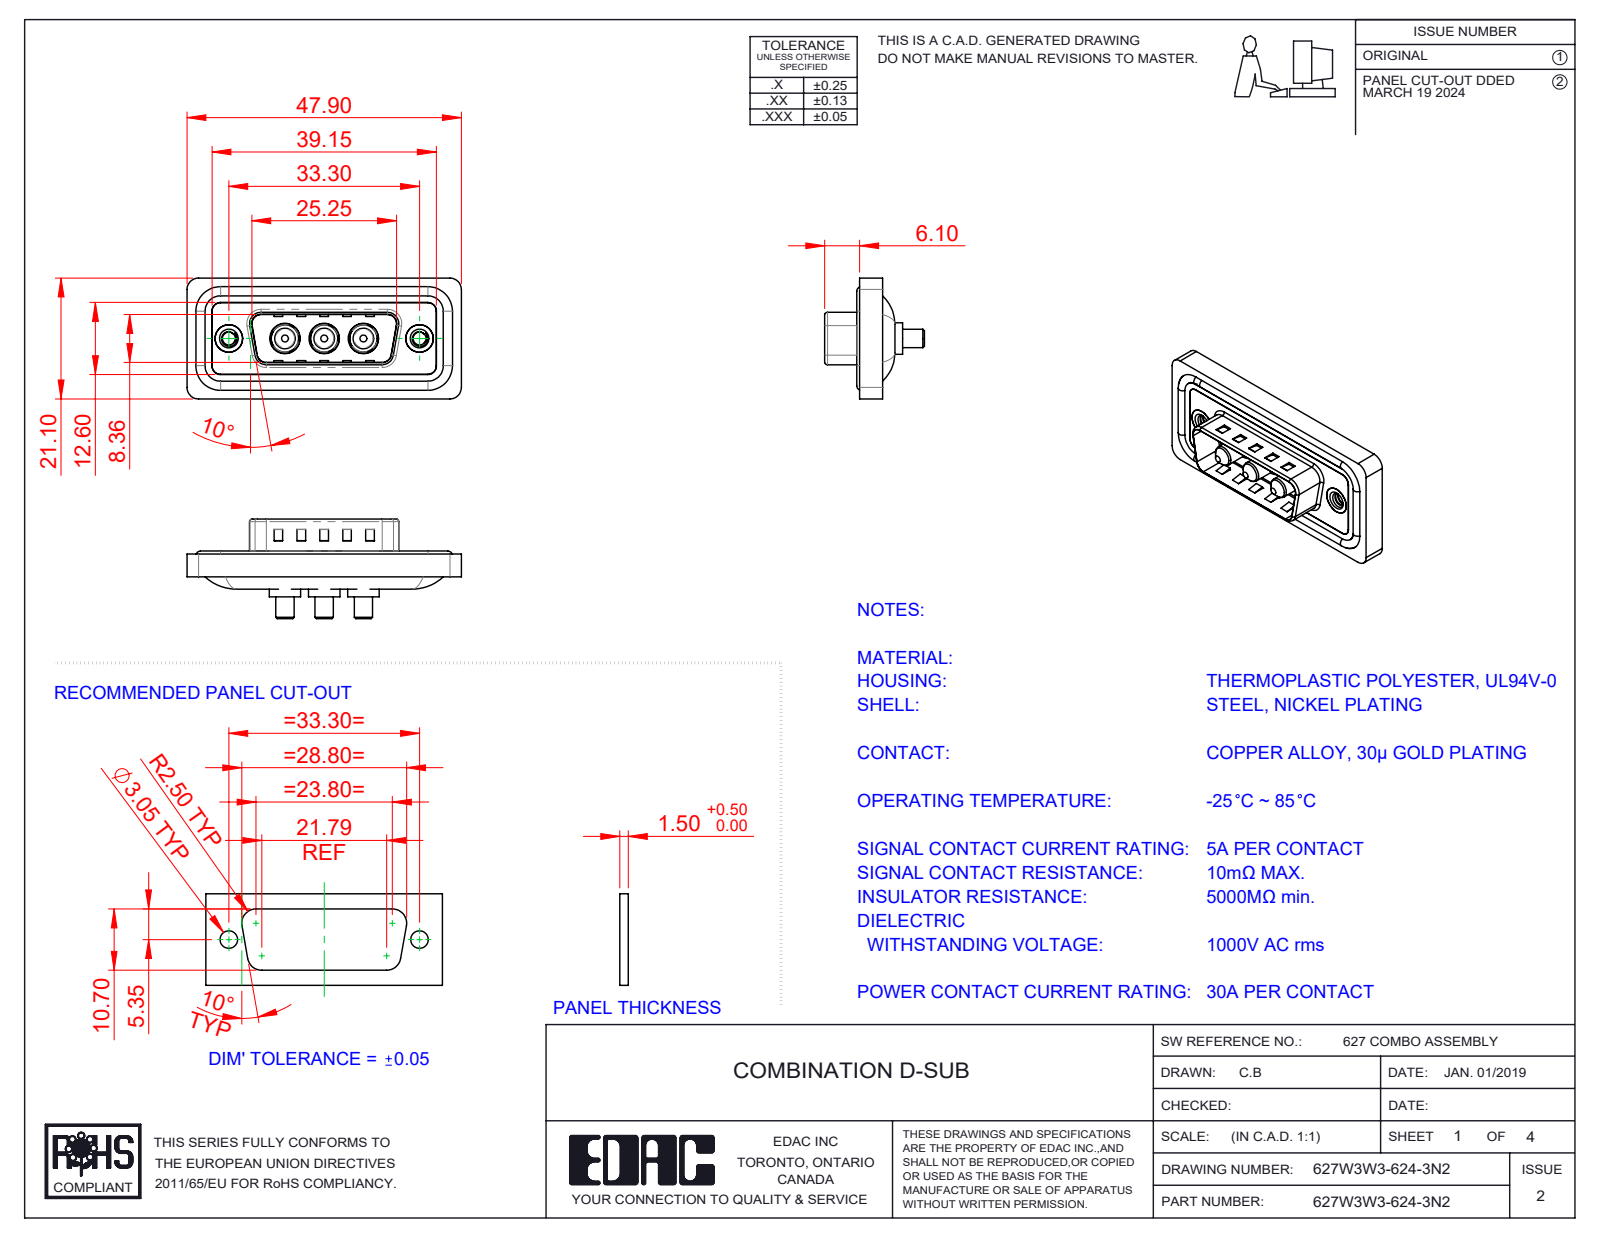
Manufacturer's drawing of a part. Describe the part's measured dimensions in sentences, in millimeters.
The part is named "627W3W3-624-3N2; 627Combo Shell Rear_15 Contacts; 627Combo Threaded Rivet_2; Power Pin_30A S (+3 more)". Its 3-D file was written by "SolidWorks 2023 (CONFIG_CONTROL_DESIGN)". It is 13 solids with 564 faces: 207 planar, 241 cylindrical and 116 other. Overall it measures 47.9 by 21.1 by 17.4 millimeters. Its volume is 5 607 cubic millimeters and its surface area 8 767 square millimeters. Round holes: 3 of diameter 4.85, 3 of diameter 5.3, 2 of diameter 2.26, 2 of diameter 4, 2 of diameter 4.8, 2 of diameter 5. Round bosses or shafts: 4 of diameter 1.6, 3 of diameter 5.5, 3 of diameter 5.2, 3 of diameter 4.75, 3 of diameter 3.75, 3 of diameter 3.6, 3 of diameter 3.2, 2 of diameter 4.9. Partial cylindrical surfaces (rounded edges, fillets, slot ends): 26 of radius 1.5, 20 of radius 2, 8 of radius 0.5, 8 of radius 1.6, 4 of radius 0.25, 4 of radius 0.6, 4 of radius 0.65, 4 of radius 0.9. The main face-to-face distances are 0.4, 1.1, 1.5, 0.5, 1.6, 3.1, 2.9, 4, 0.82, 9.58. The hole center spacings are 6.85, 9.8, 16.65, 23.5, 13.7, 33.3.
